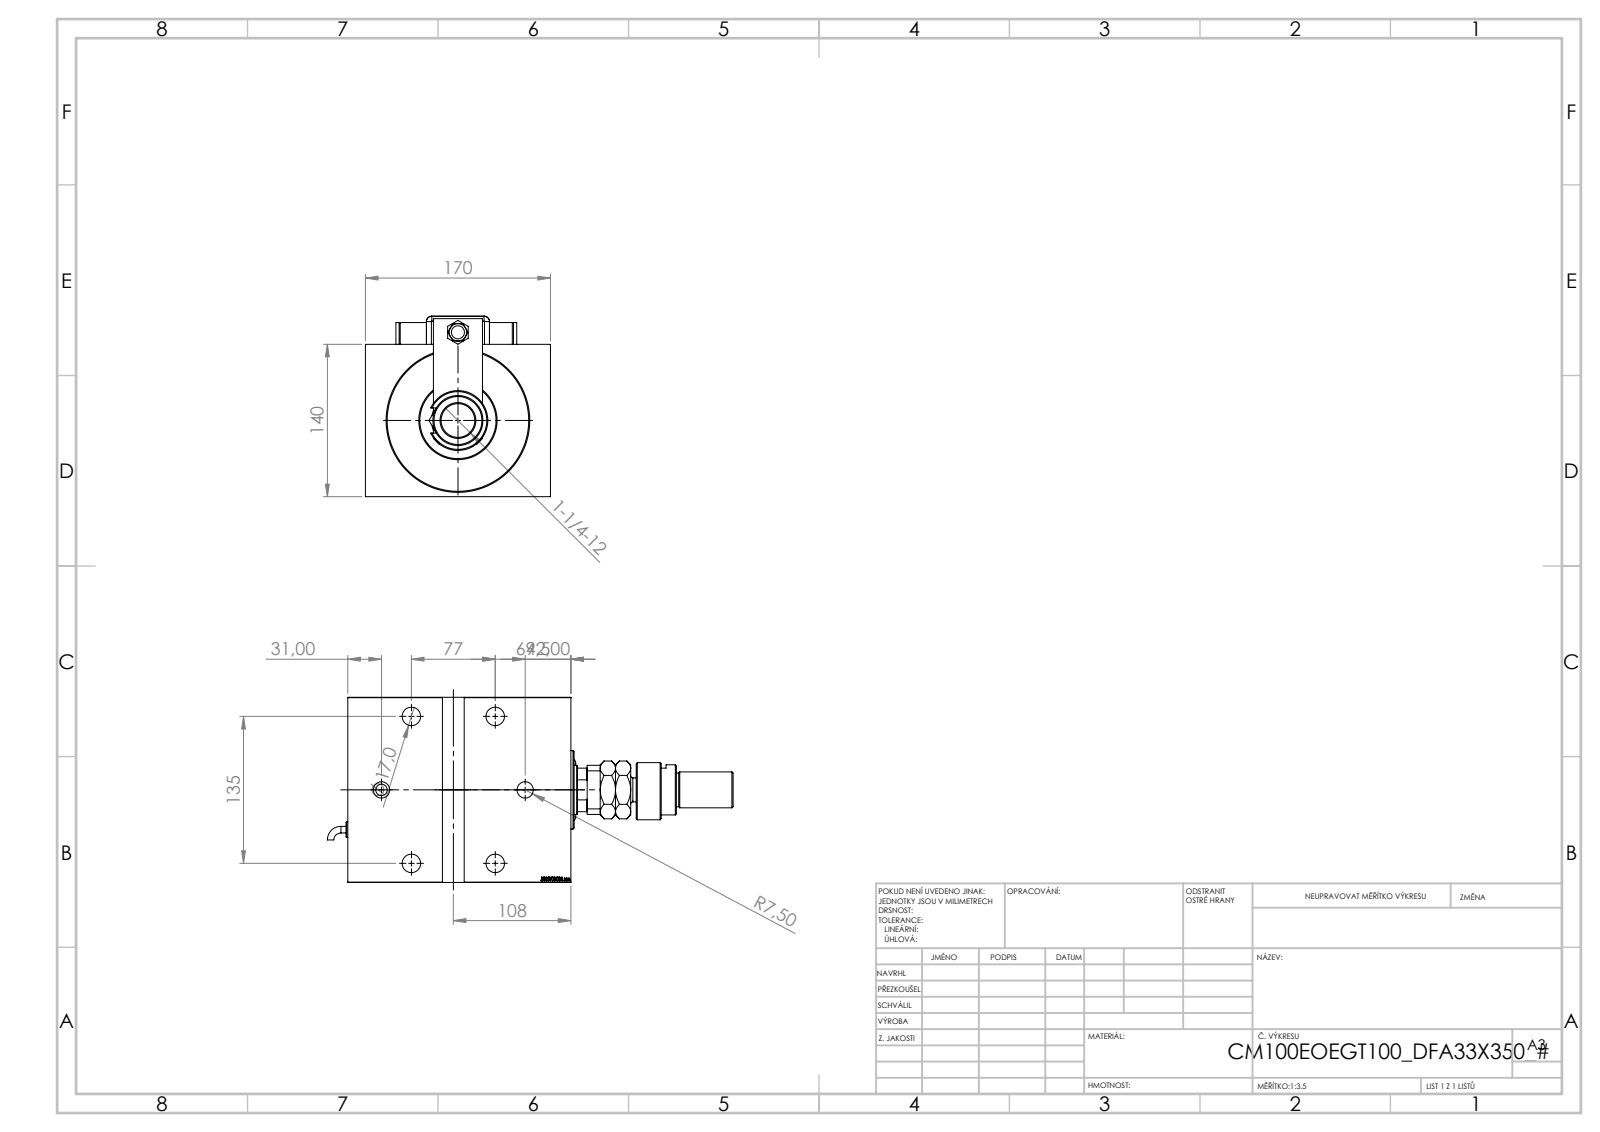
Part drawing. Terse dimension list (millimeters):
name: V450CM_E_VCP; MAGNETIC SWITCH Q; V450CM_VC_B; SWITCH_Q_FRONT_BACK (+8 more)
written by: SolidWorks 2019 (CONFIG_CONTROL_DESIGN)
unit: mm
bodies: 15 solids, 1318 faces (643 planar, 114 cylindrical, 561 other)
size: 372.76 × 170 × 165.8
volume: 4 474 000 mm³; area: 473 593 mm²
holes: 4× ⌀17, 4× ⌀25, 2× ⌀4, 2× ⌀8, 2× ⌀15, 1× ⌀12, 1× ⌀13, 1× ⌀14, 1× ⌀31.5, 1× ⌀33, 1× ⌀39, 1× ⌀45
bosses: 3× ⌀20, 2× ⌀16, 2× ⌀14, 2× ⌀6, 1× ⌀102, 1× ⌀72, 1× ⌀55, 1× ⌀46
rounds: 9× R5, 1× R10, 1× R11.5, 1× R22
face distances: 140, 170, 205, 3, 26, 179, 5, 200, 174, 165.8
hole spacings: 72.89, 124.4, 37.36, 77, 85.67, 100.19, 135, 151.81
